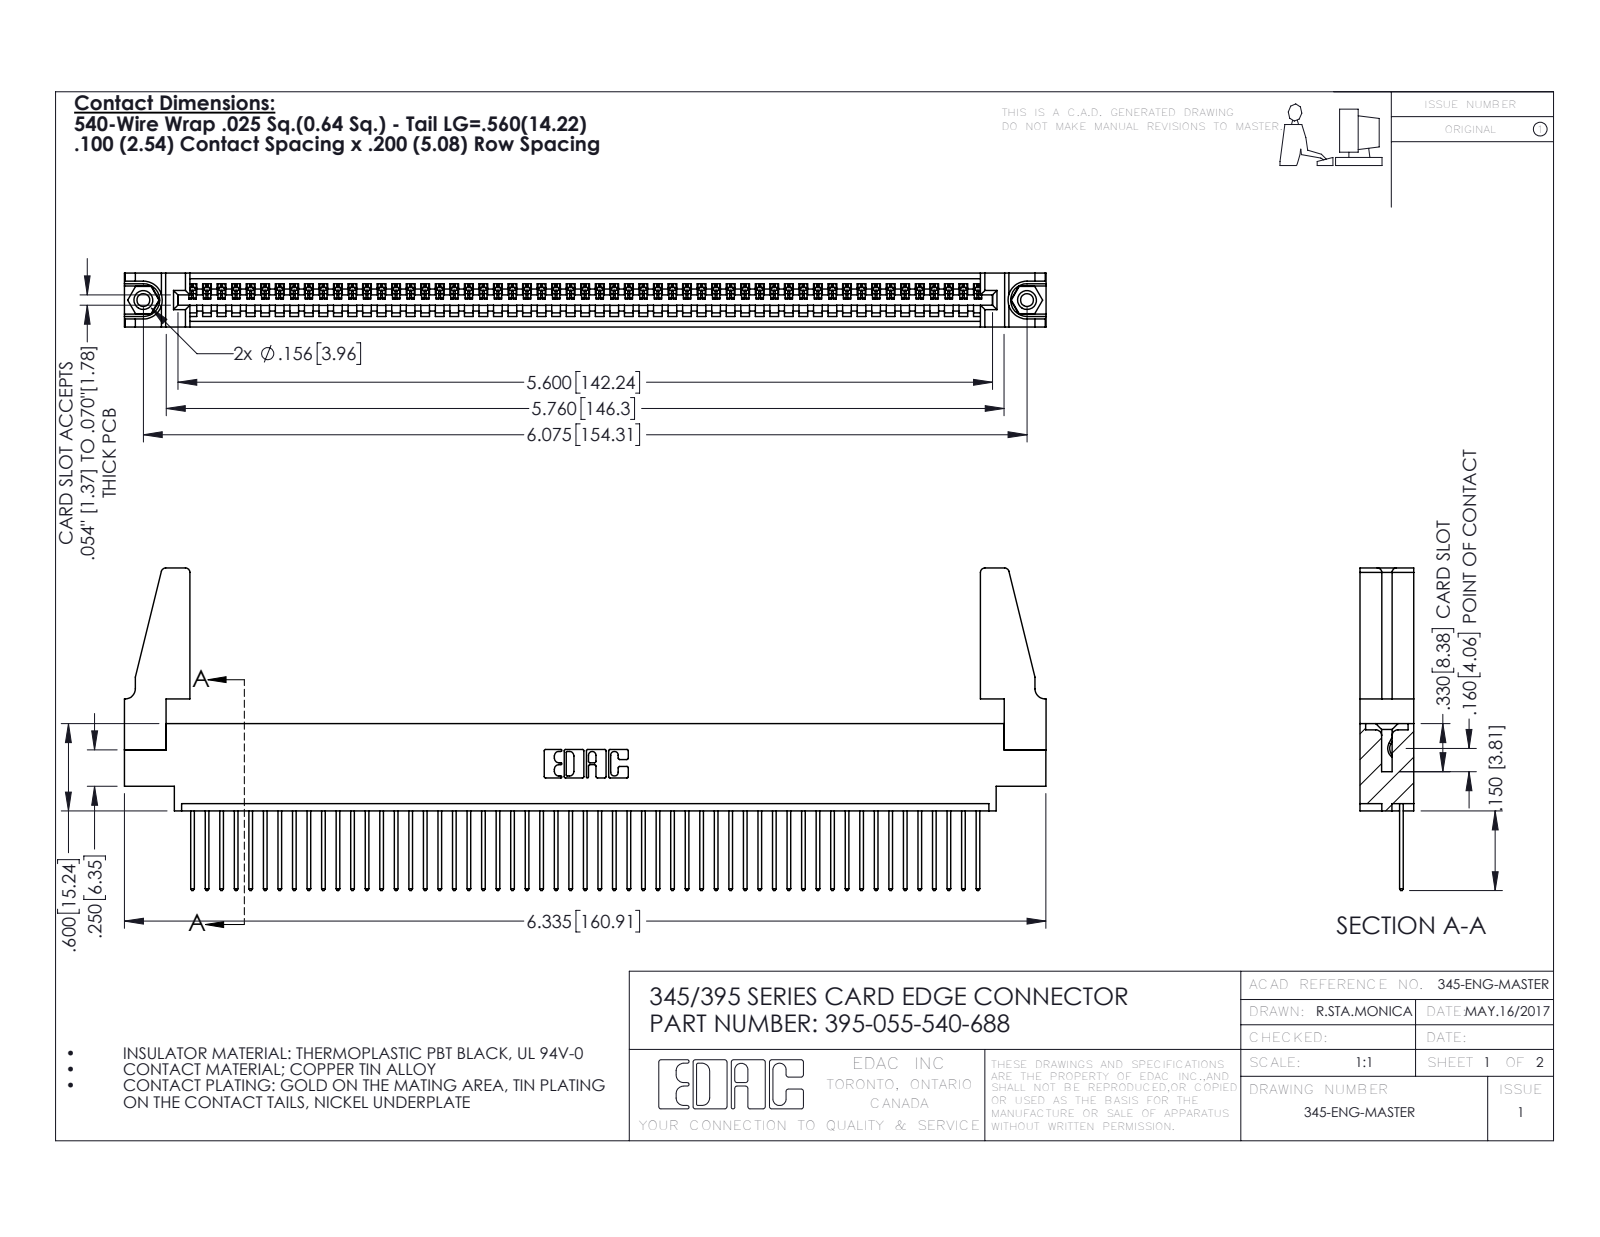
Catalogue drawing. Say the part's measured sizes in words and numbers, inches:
The part is named "345-250-001_345-250-001-102; 345 Part_0.170 Offset - 0.156 Dia-TH; 345-220-078_345-220-088; 395-055-540-688 (+1 more)". Its 3-D file was written by "SolidWorks 2016 (CONFIG_CONTROL_DESIGN)". It is 60 solids with 3444 faces: 2356 planar, 1072 cylindrical and 16 other. Overall it measures 6.336 by 2.217 by 0.37 inches. Its volume is 1.135 cubic inches and its surface area 37.78 square inches. Round holes: 2 of diameter 0.089, 2 of diameter 0.125, 2 of diameter 0.156, 1 of diameter 0.064. Round bosses or shafts: 2 of diameter 0.155. Partial cylindrical surfaces (rounded edges, fillets, slot ends): 110 of radius 0.006, 110 of radius 0.01, 22 of radius 0.01, 8 of radius 0.03, 6 of radius 0.007, 6 of radius 0.031, 3 of radius 0.026, 2 of radius 0.031. The main face-to-face distances are 0.072, 0.298, 0.37, 0.098, 0.272, 0.025, 0.2, 0.225, 0.175, 0.149. The hole center spacings are 0.27, 5.839, 6.075.
